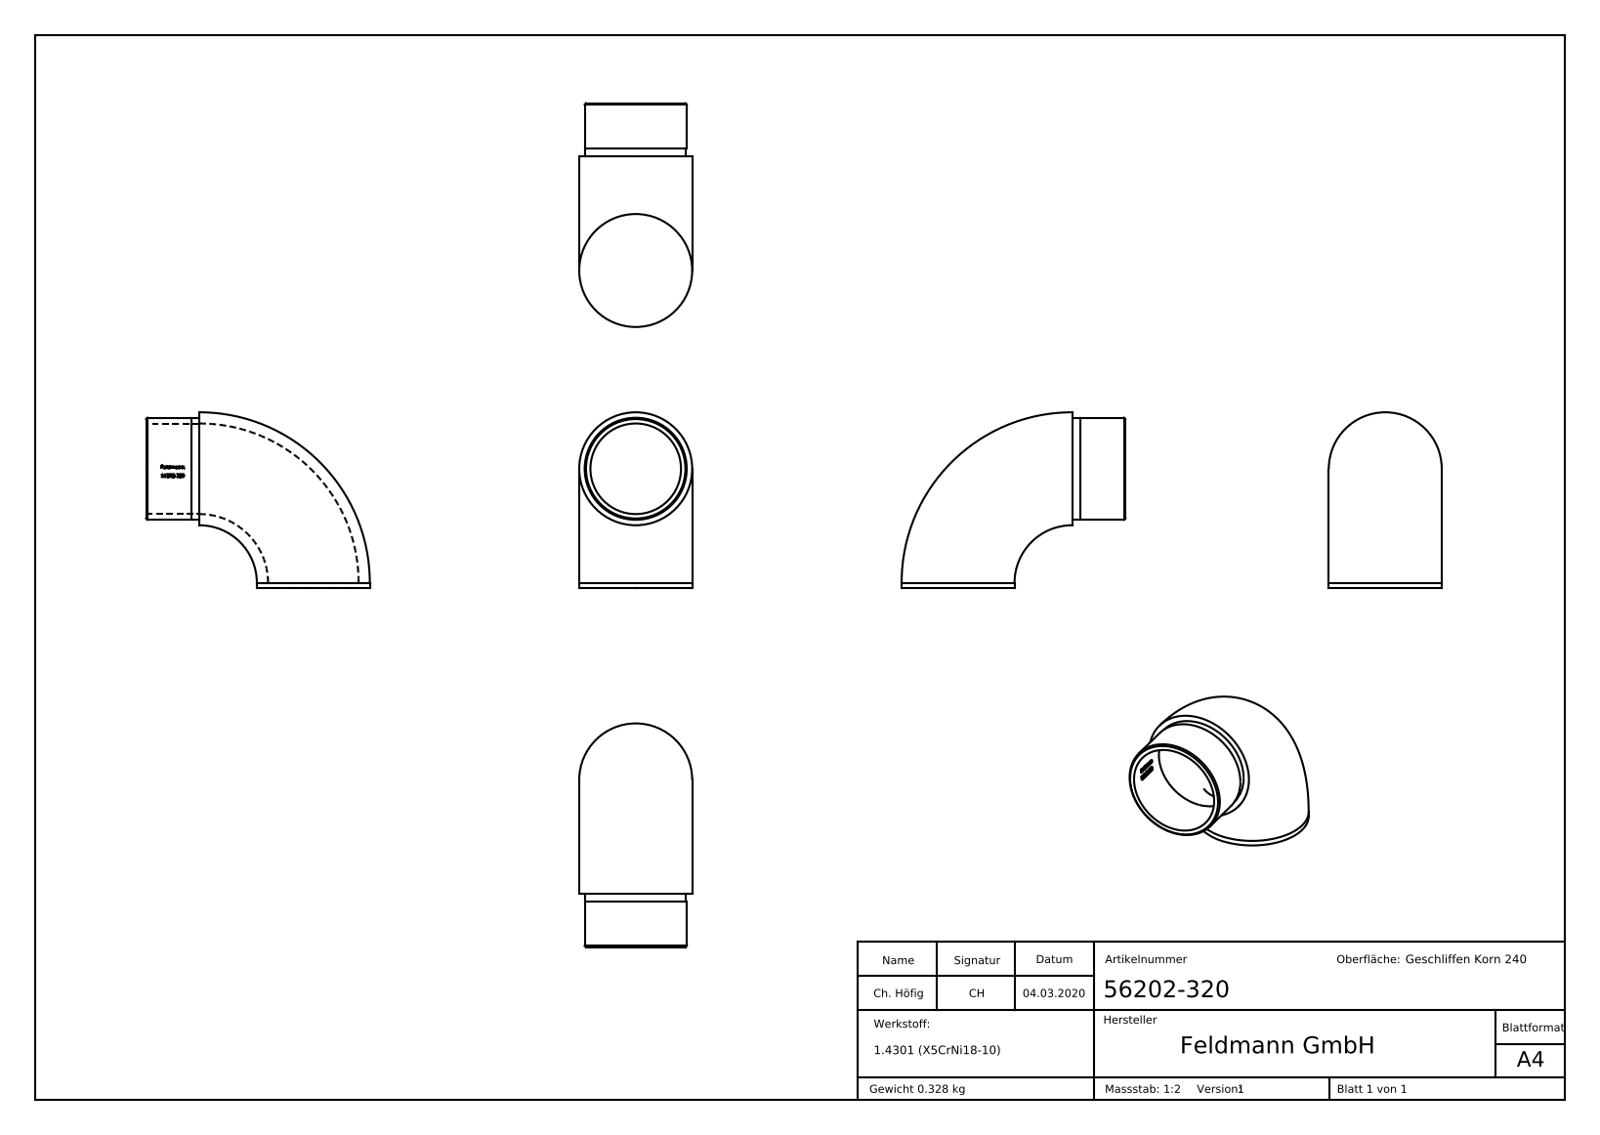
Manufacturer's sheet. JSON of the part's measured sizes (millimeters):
{"part_name": "56202-320", "step_written_by": "SolidWorks 2015 (CONFIG_CONTROL_DESIGN)", "units": "millimeters", "bodies": {"solids": 1, "faces": 238, "planar": 93, "cylindrical": 27, "other": 118}, "overall_size": [84, 66, 42.4], "volume_mm3": 41506, "surface_area_mm2": 23788, "round_holes": [[34, 1]], "round_bosses_or_shafts": [[42.4, 1], [38.3, 1], [37.9, 1]], "partial_cylinders_radius": [[17.1, 1]], "face_to_face_distances": [2, 20, 3, 17, 0.39, 2.97, 41.6, 39.6, 1.12, 3.66]}
